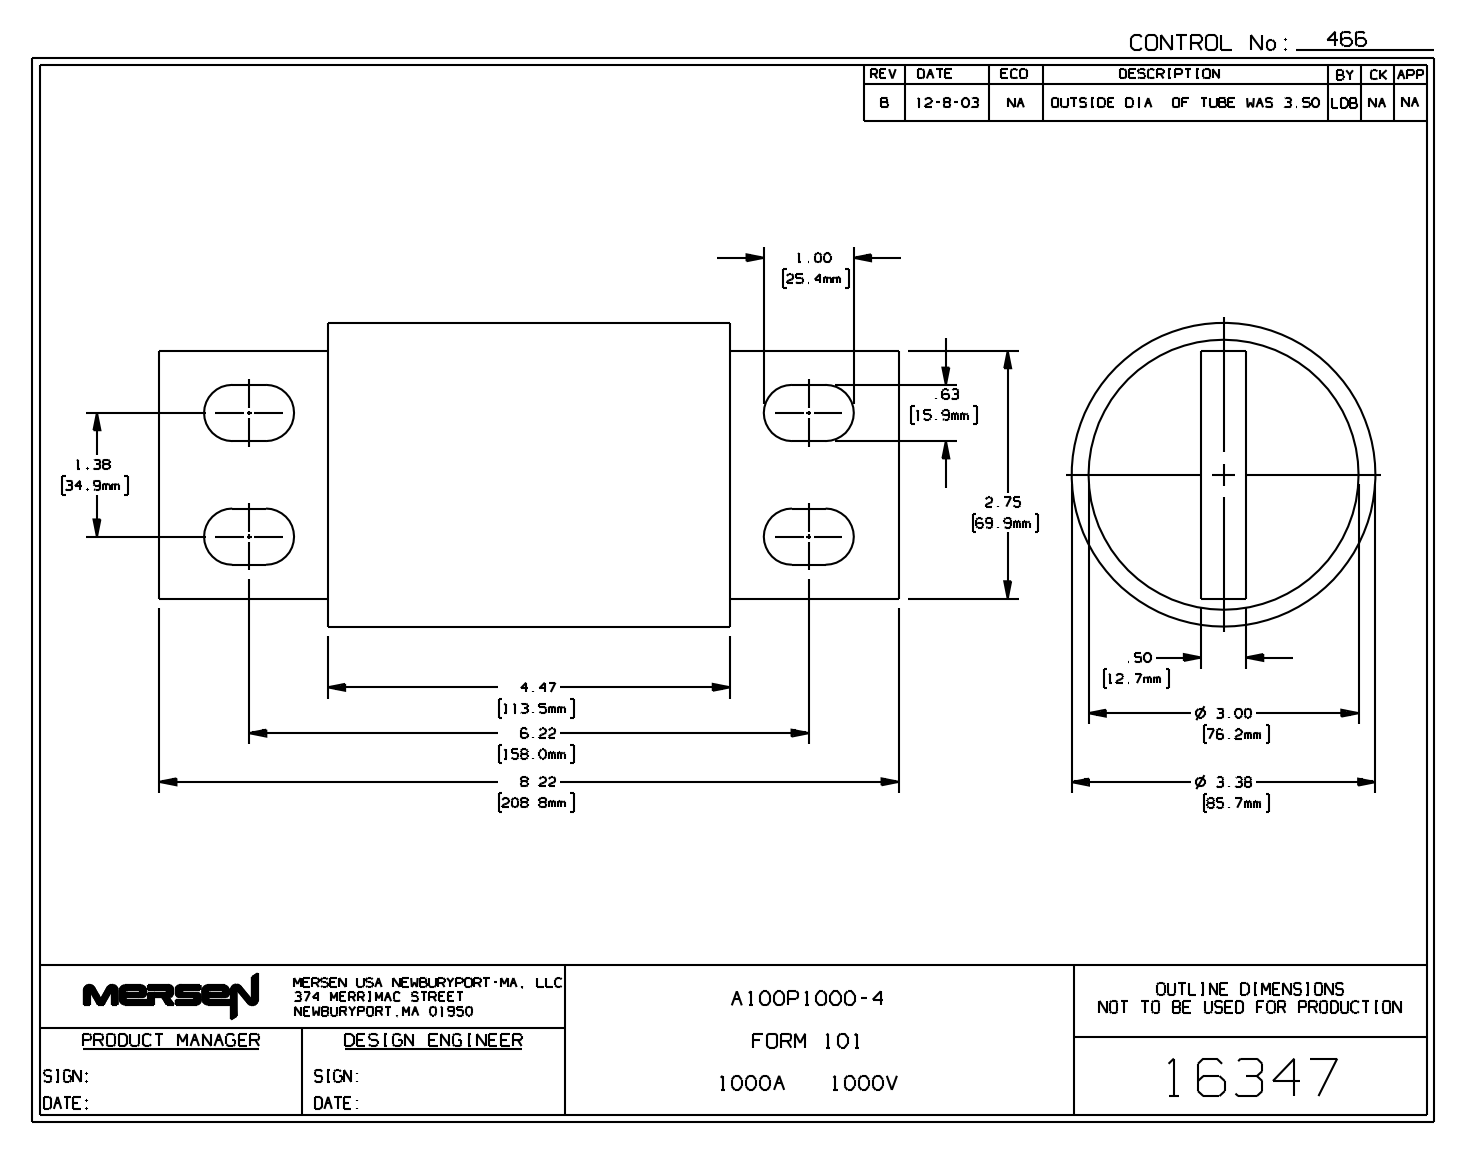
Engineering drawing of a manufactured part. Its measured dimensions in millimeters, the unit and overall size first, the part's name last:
Units: millimetres
Overall size (bounding box): 208.8 × 85.7 × 85.7
Round holes (diameter × count): ⌀3.5 ×2, ⌀5.2 ×2, ⌀6.4 ×2, ⌀76.2 ×1
Round bosses / shafts (diameter × count): ⌀6.5 ×2, ⌀85.7 ×1, ⌀76.1 ×1
Partial cylindrical surfaces — rounded edges, fillets, slot ends (radius × count): R7.9 ×8
Main face-to-face distances: 23.8, 89.7, 113.5, 12.7, 65.9, 9.6, 19.1, 22.2, 91.3, 1.6
Hole centre spacings: 34.3, 19.1, 28.6, 38.1, 57.2
Volume: 414 400 mm³ · Surface area: 118 500 mm²
Bodies: 9 solids, 282 faces (146 planar, 56 cylindrical, 80 other)
Part name (STEP PRODUCT): 16347revb
STEP written by: SolidWorks 2013 (AUTOMOTIVE_DESIGN)
